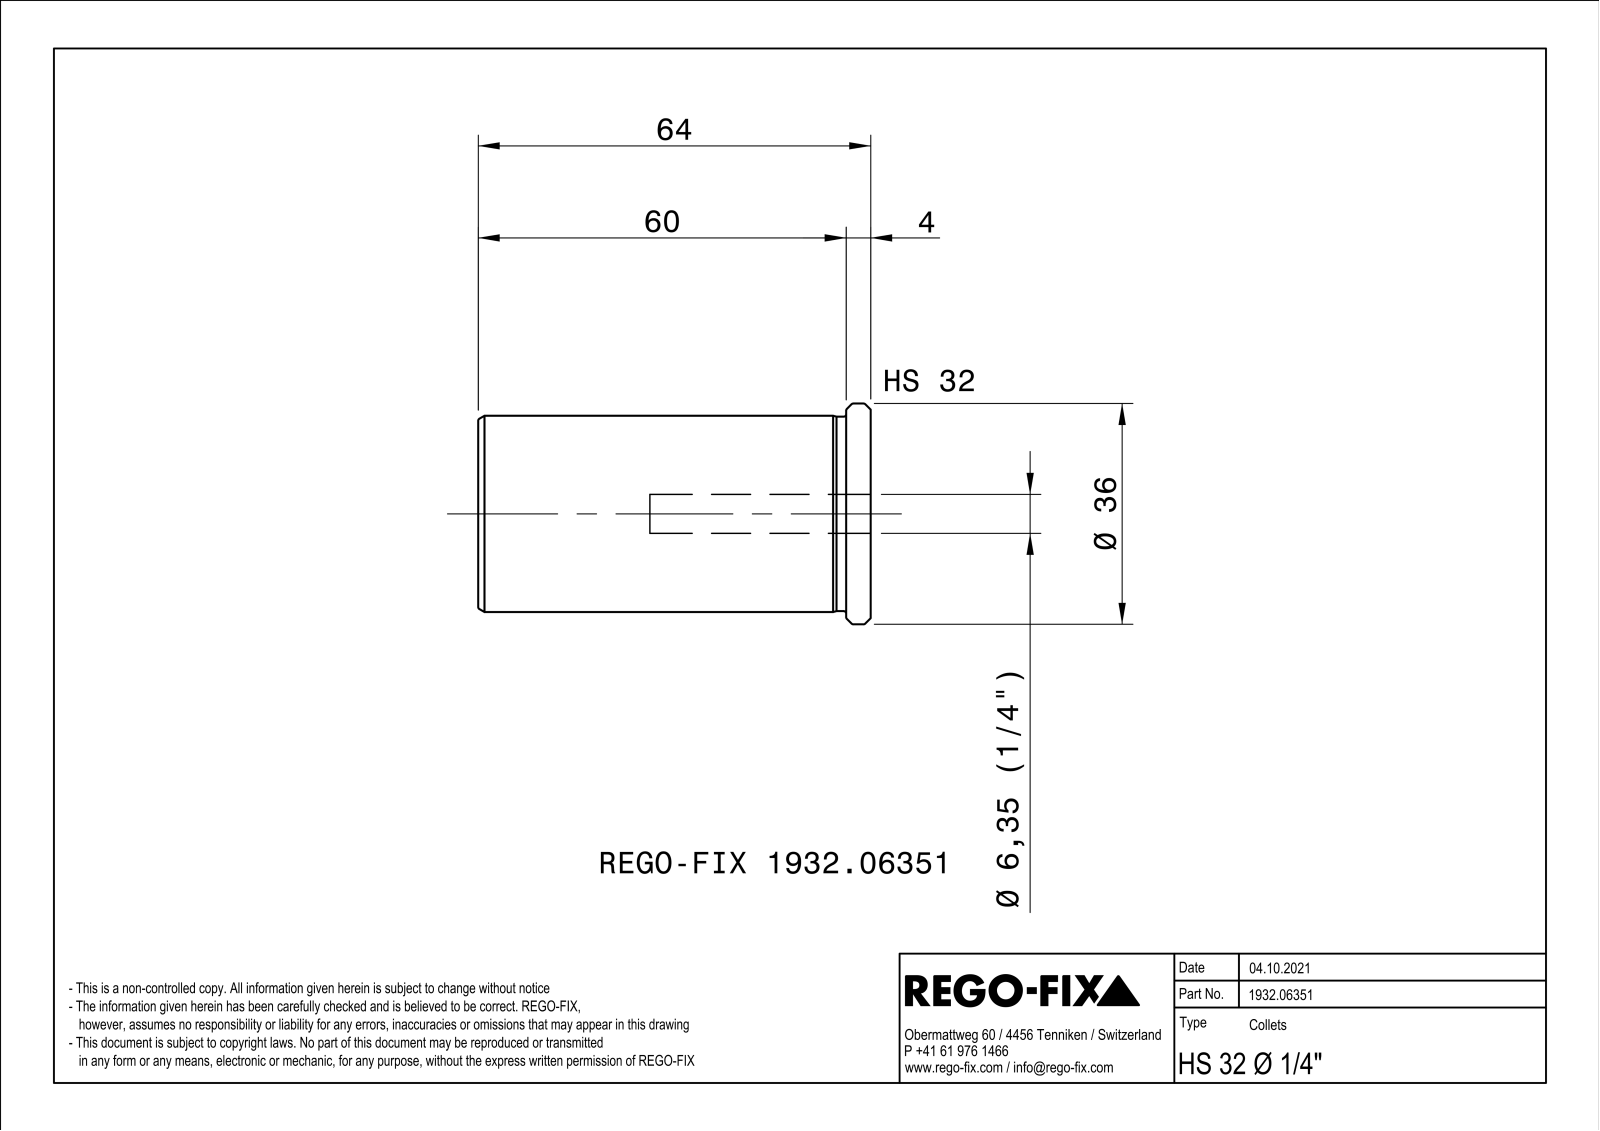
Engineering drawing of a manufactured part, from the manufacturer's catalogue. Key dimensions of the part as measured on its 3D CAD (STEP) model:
Part name (STEP PRODUCT): NOCUT
STEP written by: SIEMENS PLM Software Solid Edge ST10 (AUTOMOTIVE_DESIGN)
Units: millimetres
Bodies: 1 solid, 72 faces (22 planar, 12 cylindrical, 38 other)
Overall size (bounding box): 64 × 35.99 × 35.99
Volume: 39 485 mm³ · Surface area: 14 260 mm²
Round holes (diameter × count): ⌀6.35 ×1, ⌀10 ×1, ⌀26.5 ×1
Round bosses / shafts (diameter × count): ⌀36 ×1, ⌀32 ×1, ⌀31.7 ×1
Main face-to-face distances: 1, 64, 4, 60
